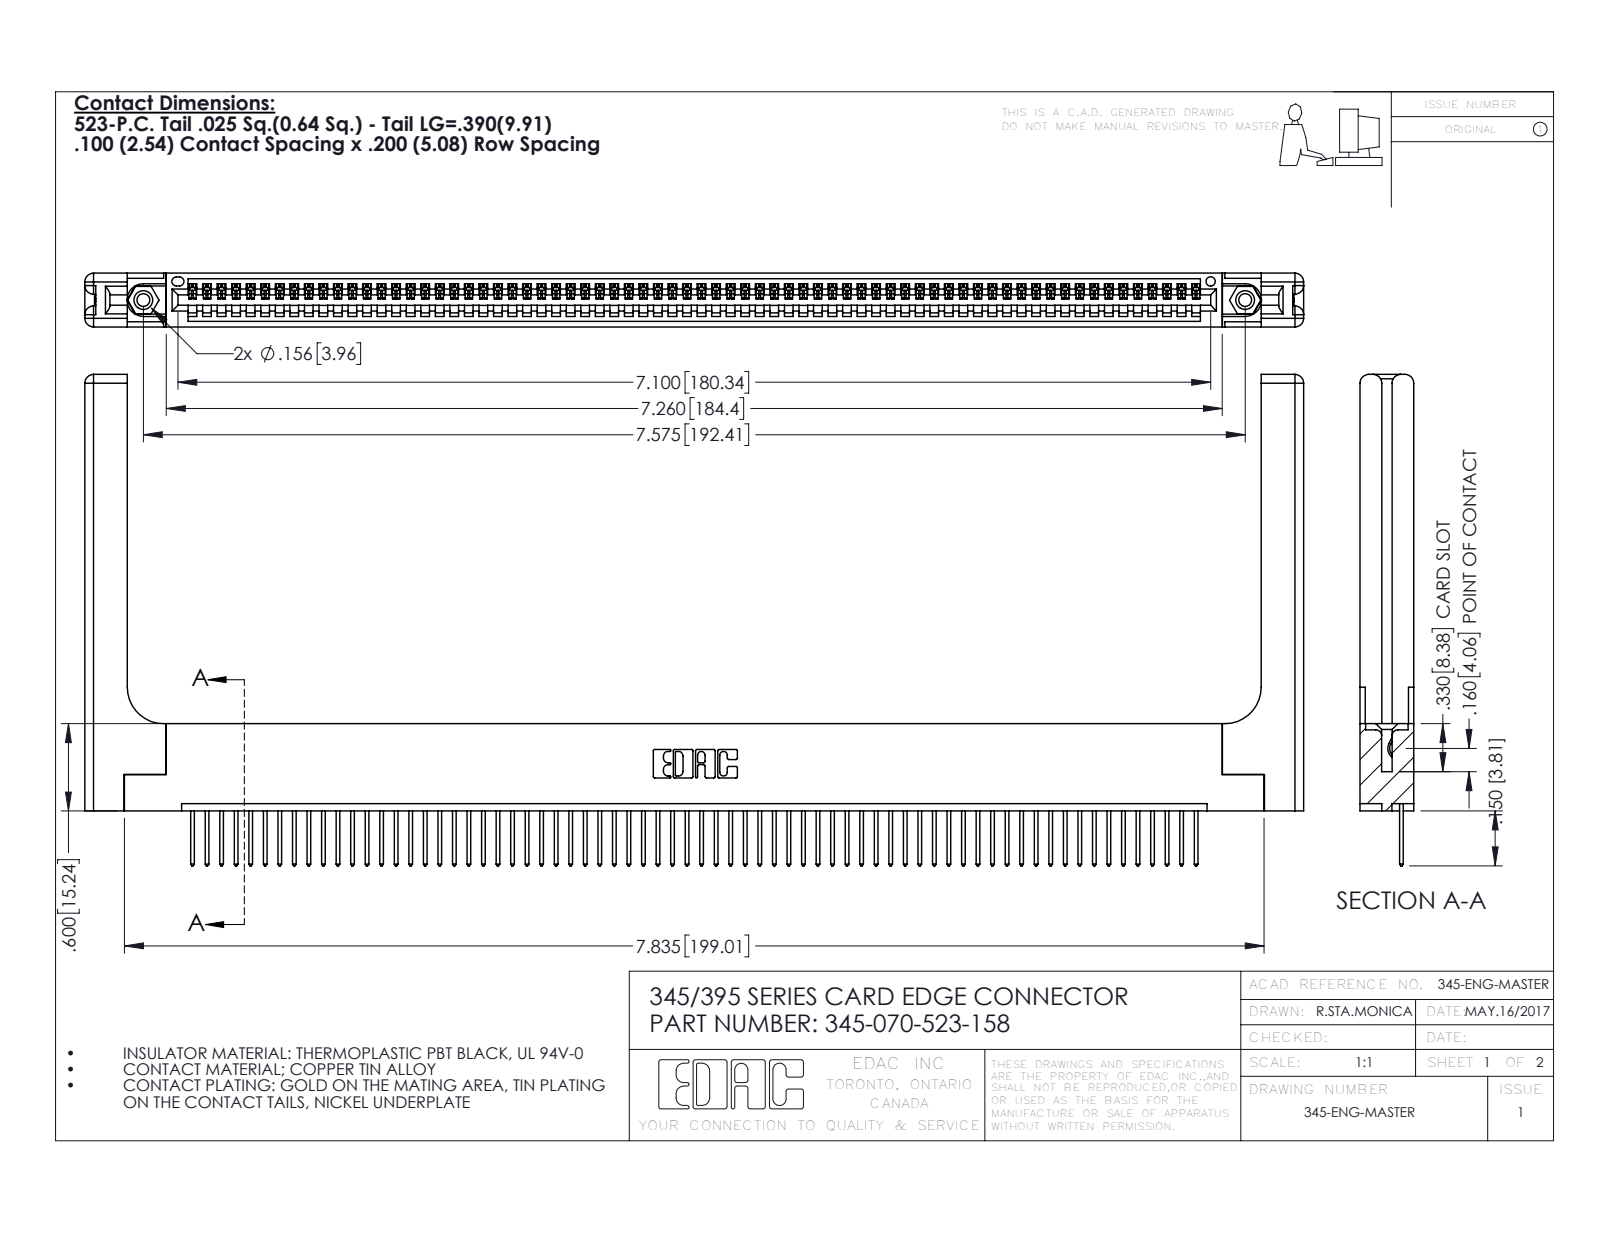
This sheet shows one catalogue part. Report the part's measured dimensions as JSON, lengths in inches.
{"part_name": "345 Part_Flush Mounting Lugs - 0.156 Dia-TH; 345-220-058_345-220-058; 345-250-001_345-250-001-102; 345-292-001_345-293-123 (+1 more)", "step_written_by": "SolidWorks 2016 (CONFIG_CONTROL_DESIGN)", "units": "inches", "bodies": {"solids": 75, "faces": 4442, "planar": 3028, "cylindrical": 1354, "other": 60}, "overall_size": [8.379, 3.377, 0.37], "volume_in3": 1.765, "surface_area_in2": 50.99, "round_holes": [[0.089, 2], [0.125, 2], [0.156, 2], [0.064, 1]], "round_bosses_or_shafts": [[0.155, 2]], "partial_cylinders_radius": [[0.006, 140], [0.01, 140], [0.01, 22], [0.06, 16], [0.007, 6], [0.031, 6], [0.026, 3], [0.03, 2]], "face_to_face_distances": [0.072, 0.298, 0.37, 0.2, 0.098, 0.272, 0.025, 0.225, 0.148, 0.15], "hole_center_spacings": [0.27, 7.339, 7.575]}
